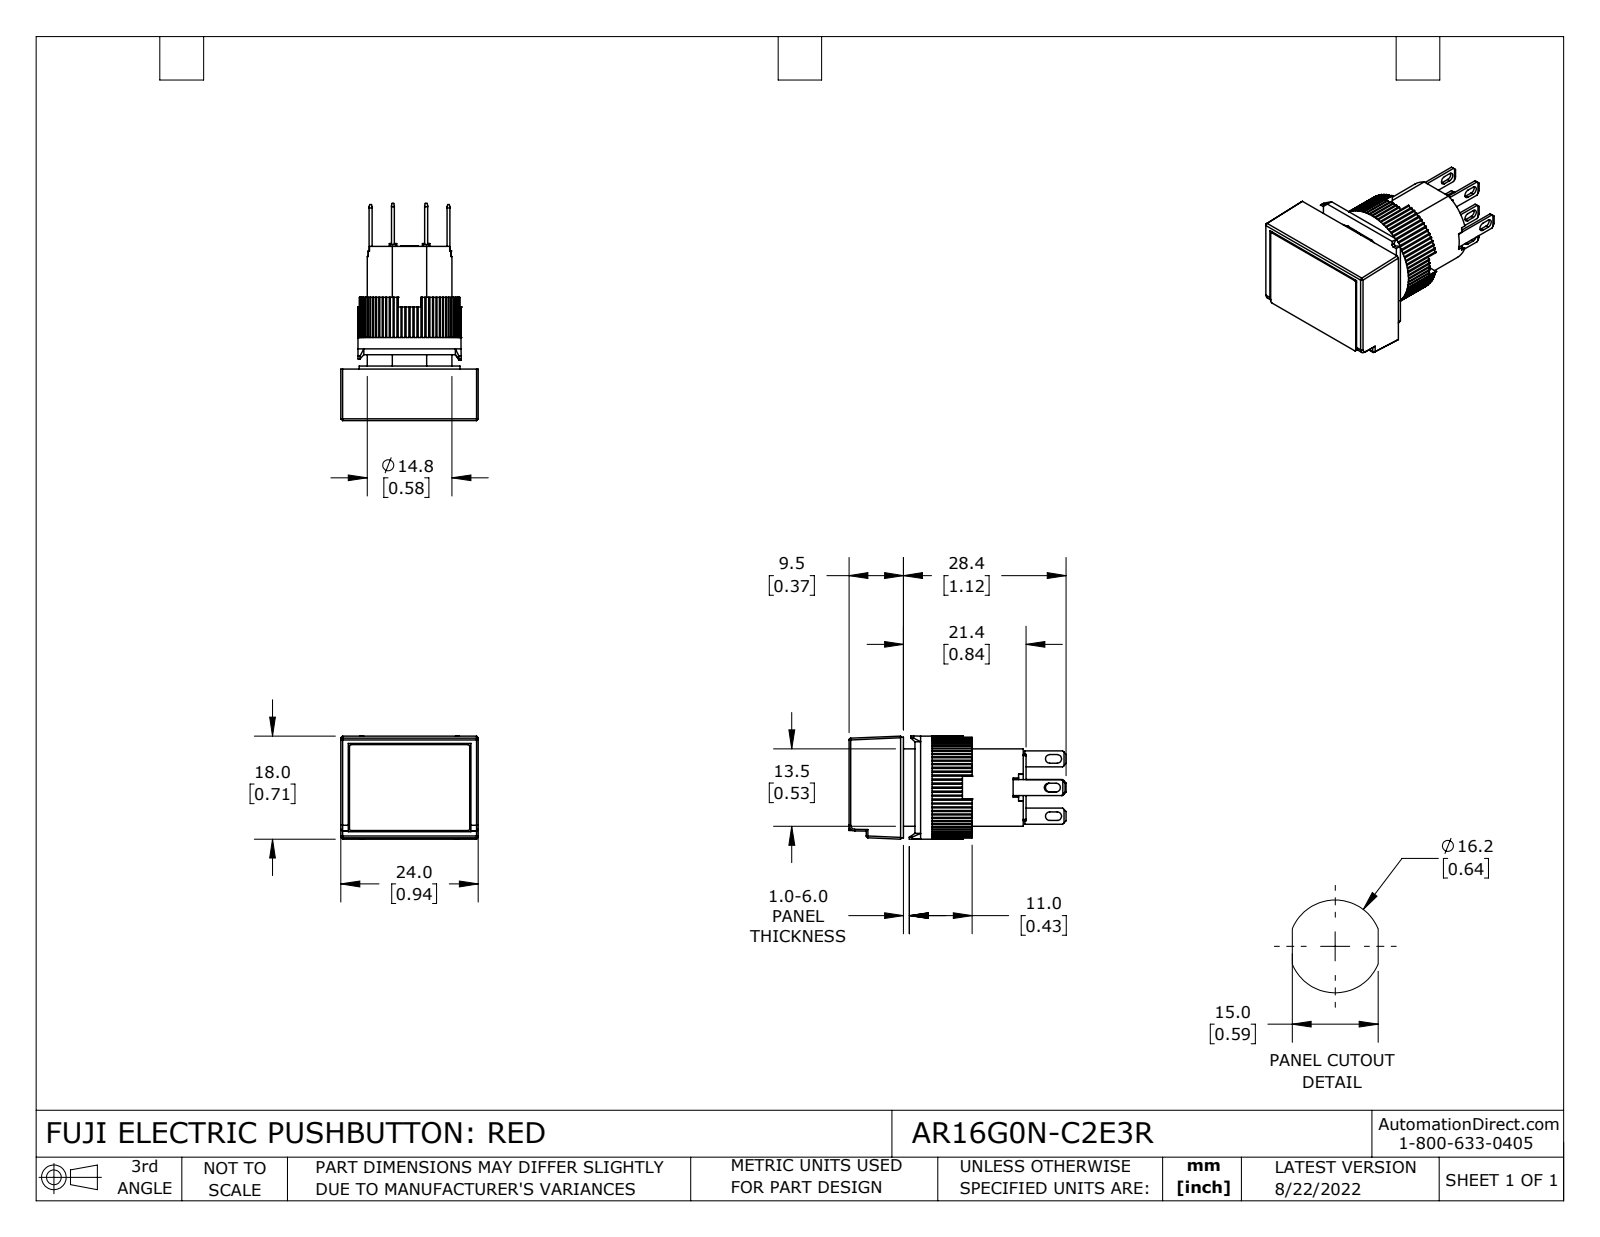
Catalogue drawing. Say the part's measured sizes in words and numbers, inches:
The part is named "AR16G0N-C2E3R". Its 3-D file was written by "SolidWorks 2021 (CONFIG_CONTROL_DESIGN)". It is 14 solids with 841 faces: 654 planar, 181 cylindrical and 6 other. Overall it measures 1.492 by 0.945 by 0.709 inches. Its volume is 0.448 cubic inches and its surface area 9.503 square inches. Round holes: 1 of diameter 0.543, 1 of diameter 0.583. Round bosses or shafts: 1 of diameter 0.709, 1 of diameter 0.693. Partial cylindrical surfaces (rounded edges, fillets, slot ends): 80 of radius 0.01, 12 of radius 0.008, 8 of radius 0.03, 6 of radius 0.012, 1 of radius 0.039. The main face-to-face distances are 0.213, 0.354, 0.142, 0.35, 0.492, 0.138, 0.02, 0.843, 0.059, 0.453.
